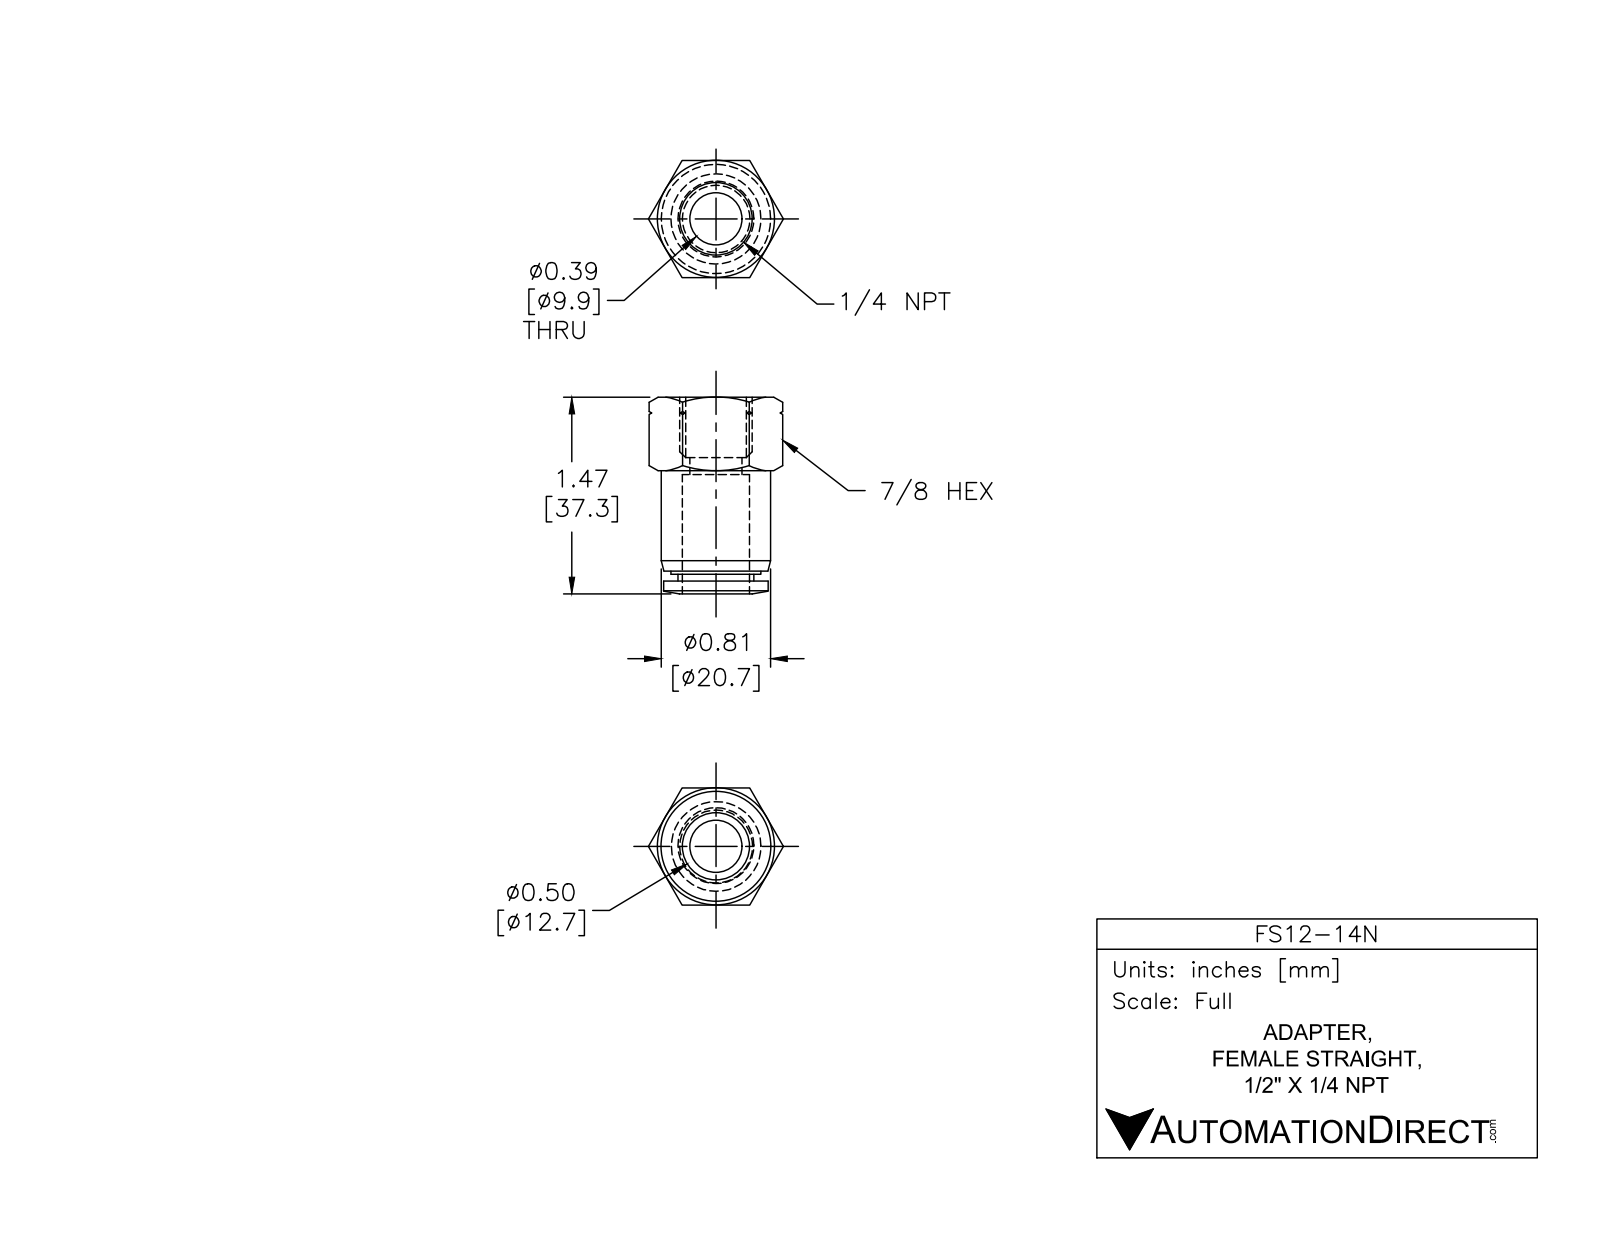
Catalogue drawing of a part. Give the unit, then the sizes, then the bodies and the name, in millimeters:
Units: millimetres
Overall size (bounding box): 37.4 × 25.4 × 22
Round holes (diameter × count): ⌀10 ×1, ⌀13 ×1
Round bosses / shafts (diameter × count): ⌀20.8 ×1, ⌀19.9 ×1, ⌀17.1 ×1, ⌀14.5 ×1
Main face-to-face distances: 22, 35, 33.1, 1.9, 33.7, 0.6, 1.3, 11.5, 21.6, 22.2
Volume: 8 500 mm³ · Surface area: 4 918 mm²
Bodies: 1 solid, 61 faces (13 planar, 12 cylindrical, 36 other)
Part name (STEP PRODUCT): FS12-14N
STEP written by: SolidWorks 2015 (AUTOMOTIVE_DESIGN)
